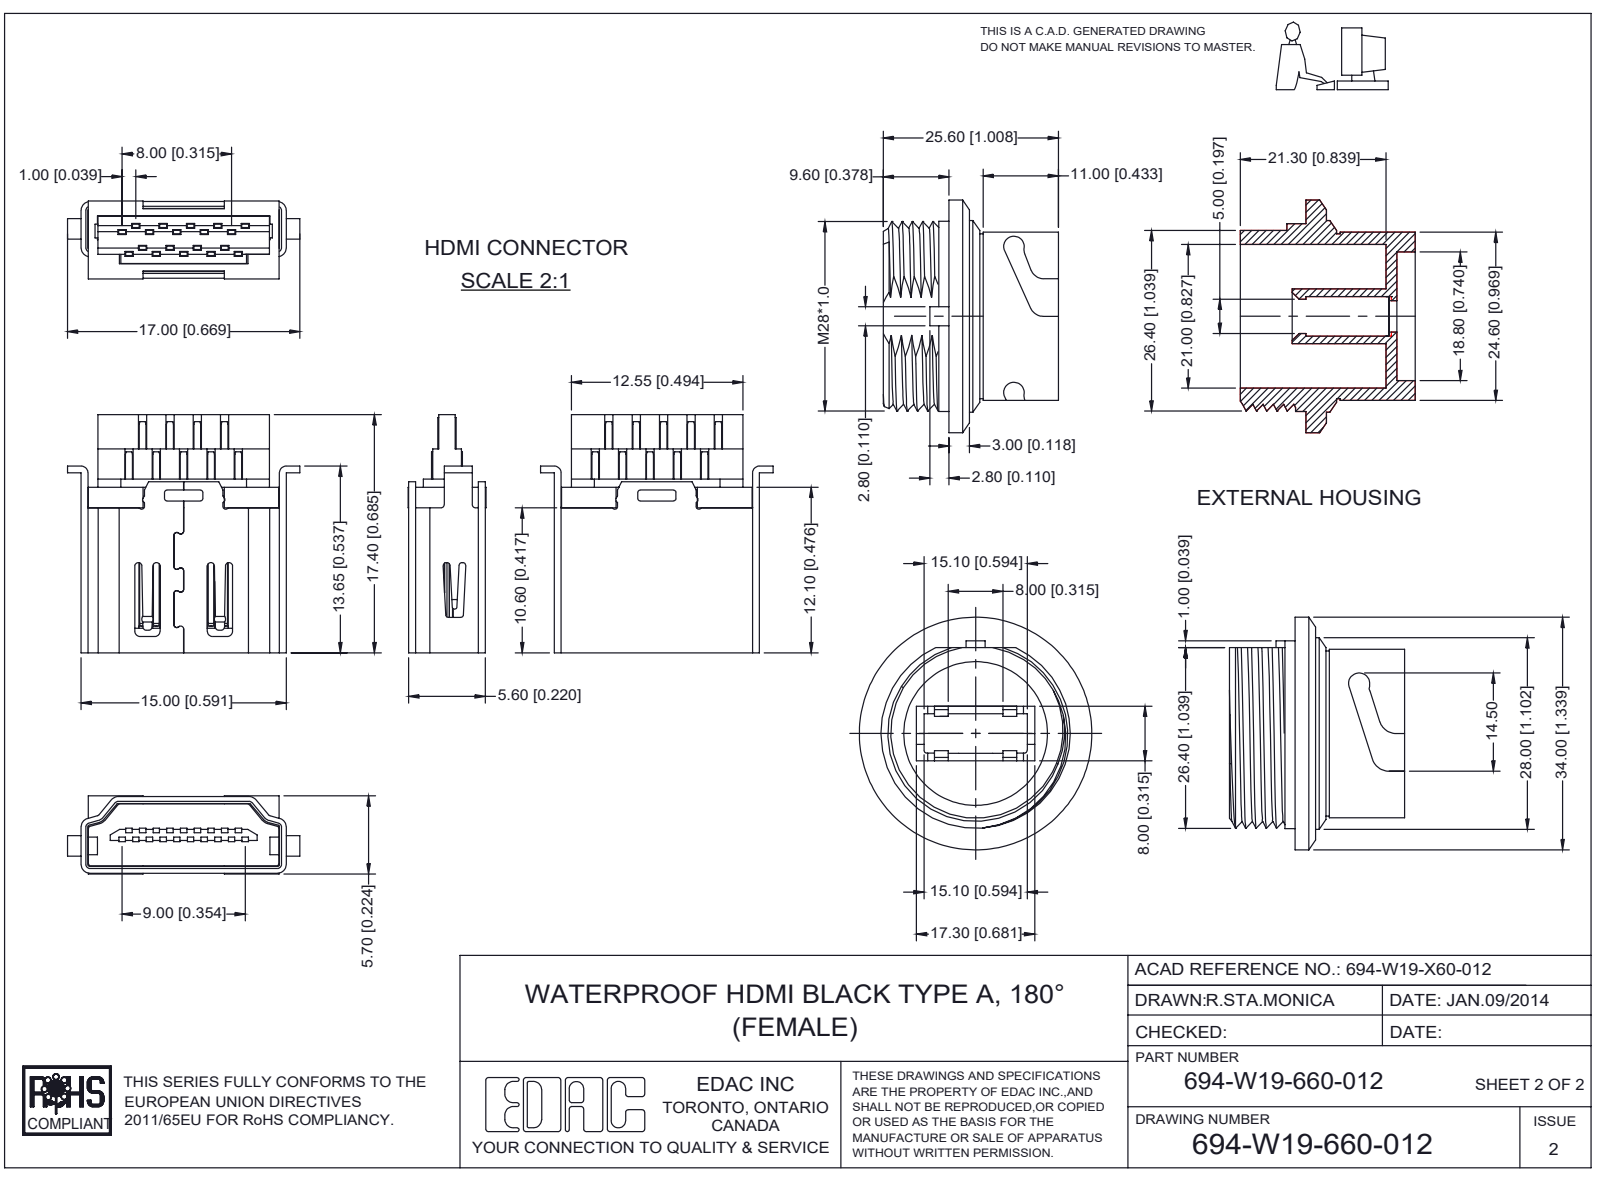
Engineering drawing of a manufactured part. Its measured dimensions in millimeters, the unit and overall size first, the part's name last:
Units: millimetres
Overall size (bounding box): 34 × 34 × 25.6
Round holes (diameter × count): ⌀18.8 ×1, ⌀21 ×1
Round bosses / shafts (diameter × count): ⌀34 ×1, ⌀28 ×1, ⌀27.8 ×1, ⌀24.6 ×1, ⌀24.1 ×1
Partial cylindrical surfaces — rounded edges, fillets, slot ends (radius × count): R0.15 ×240, R0.21 ×38, R0.2 ×28, R0.5 ×12, R0.25 ×10, R0.1 ×6, R0.35 ×6, R0.65 ×6
Main face-to-face distances: 2.7, 0.5, 1.1, 0.55, 6.9, 9.6, 3, 1.6, 1.9, 8
Volume: 7 371 mm³ · Surface area: 9 732 mm²
Bodies: 23 solids, 1962 faces (1365 planar, 542 cylindrical, 55 other)
Part name (STEP PRODUCT): 694-W19-660-012; HDMI CONTACT1 694-W19-X60-012; HDMI CONTACT2 694-W19-X60-012; HDMI SHELL 694-W19-X60-012 (+4 more)
STEP written by: SolidWorks 2020 (AUTOMOTIVE_DESIGN)
